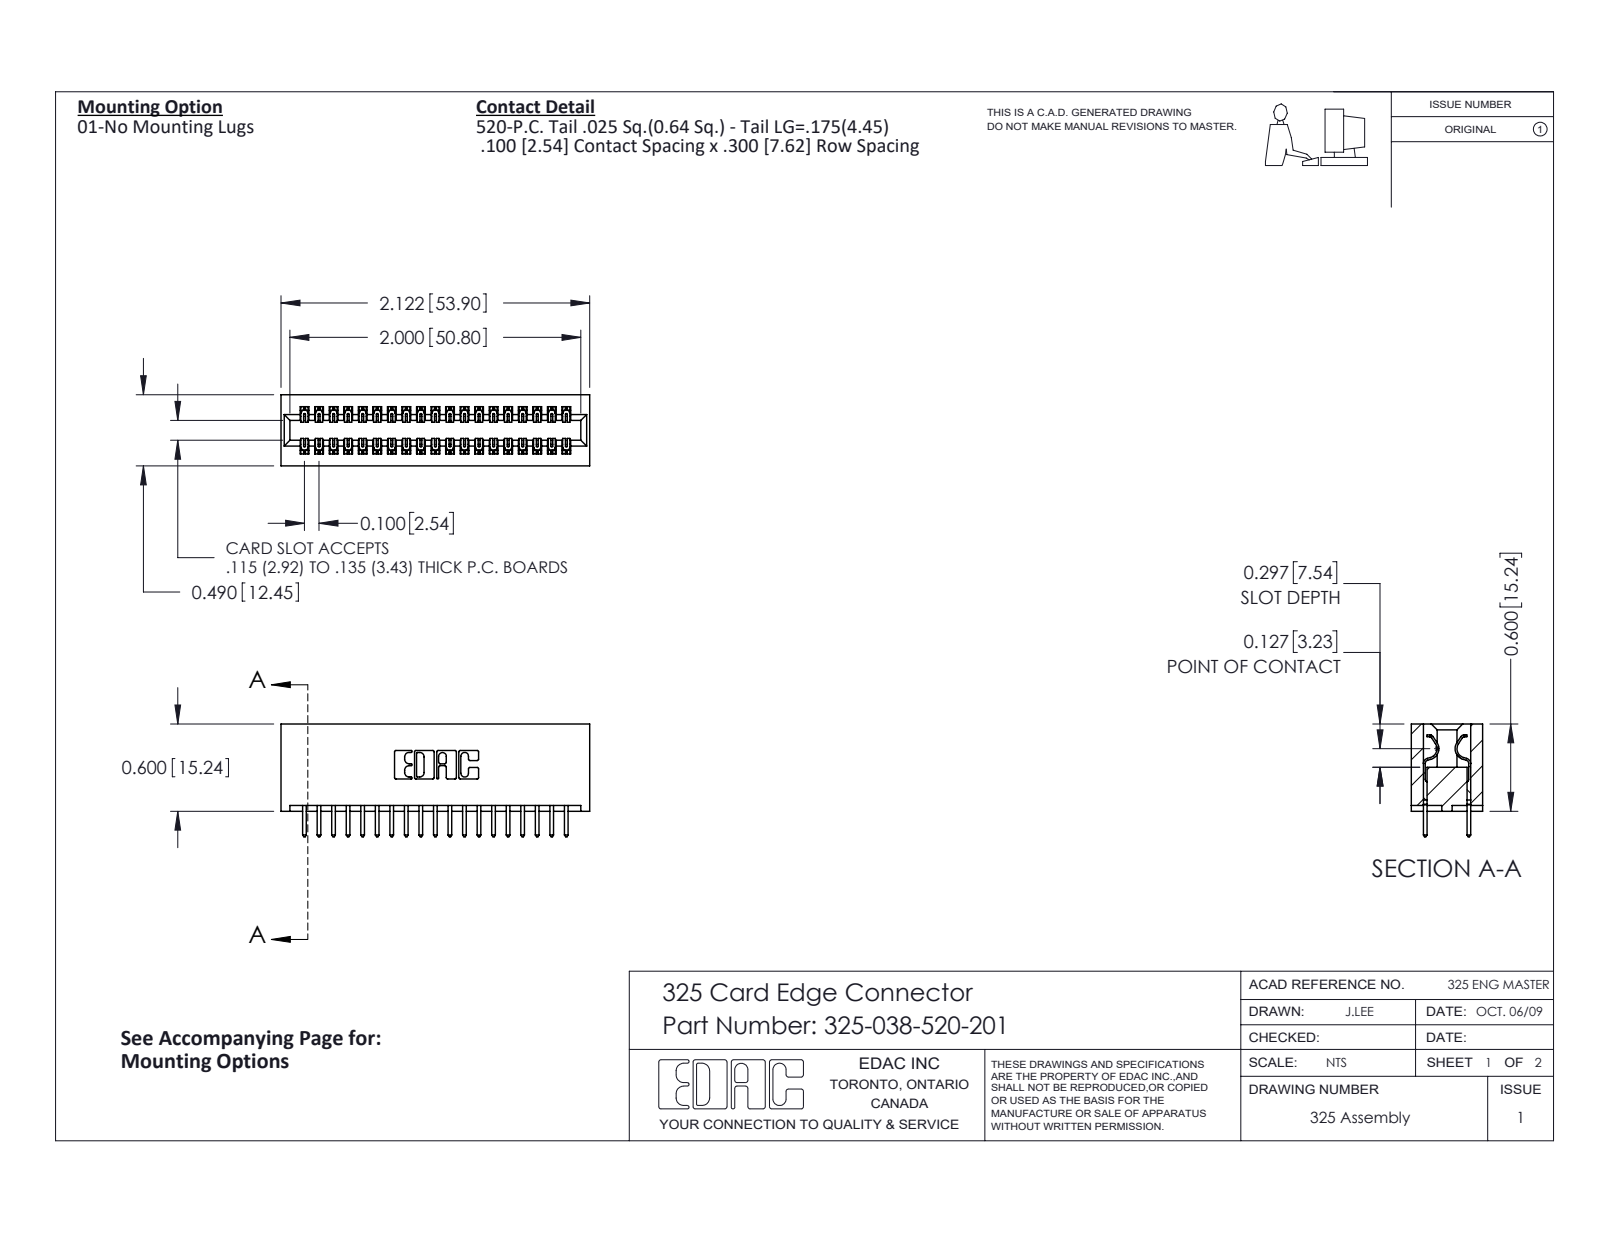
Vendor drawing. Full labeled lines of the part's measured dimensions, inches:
Part name (STEP PRODUCT): 325-038-520-201; 325 Part_Lugless; 325-292-001_325-293-120
STEP written by: SolidWorks 2016 (CONFIG_CONTROL_DESIGN)
Units: inches
Bodies: 39 solids, 2082 faces (1434 planar, 648 cylindrical, 0 other)
Overall size (bounding box): 2.122 × 0.775 × 0.49
Volume: 0.449 in³ · Surface area: 13.85 in²
Partial cylindrical surfaces — rounded edges, fillets, slot ends (radius × count): R0.006 ×57, R0.01 ×38, R0.01 ×22, R0.007 ×6, R0.031 ×6, R0.026 ×3, R0.014 ×2, R0.022 ×2
Main face-to-face distances: 0.083, 0.407, 0.3, 0.49, 0.107, 0.383, 0.025, 0.325, 0.1, 0.2
